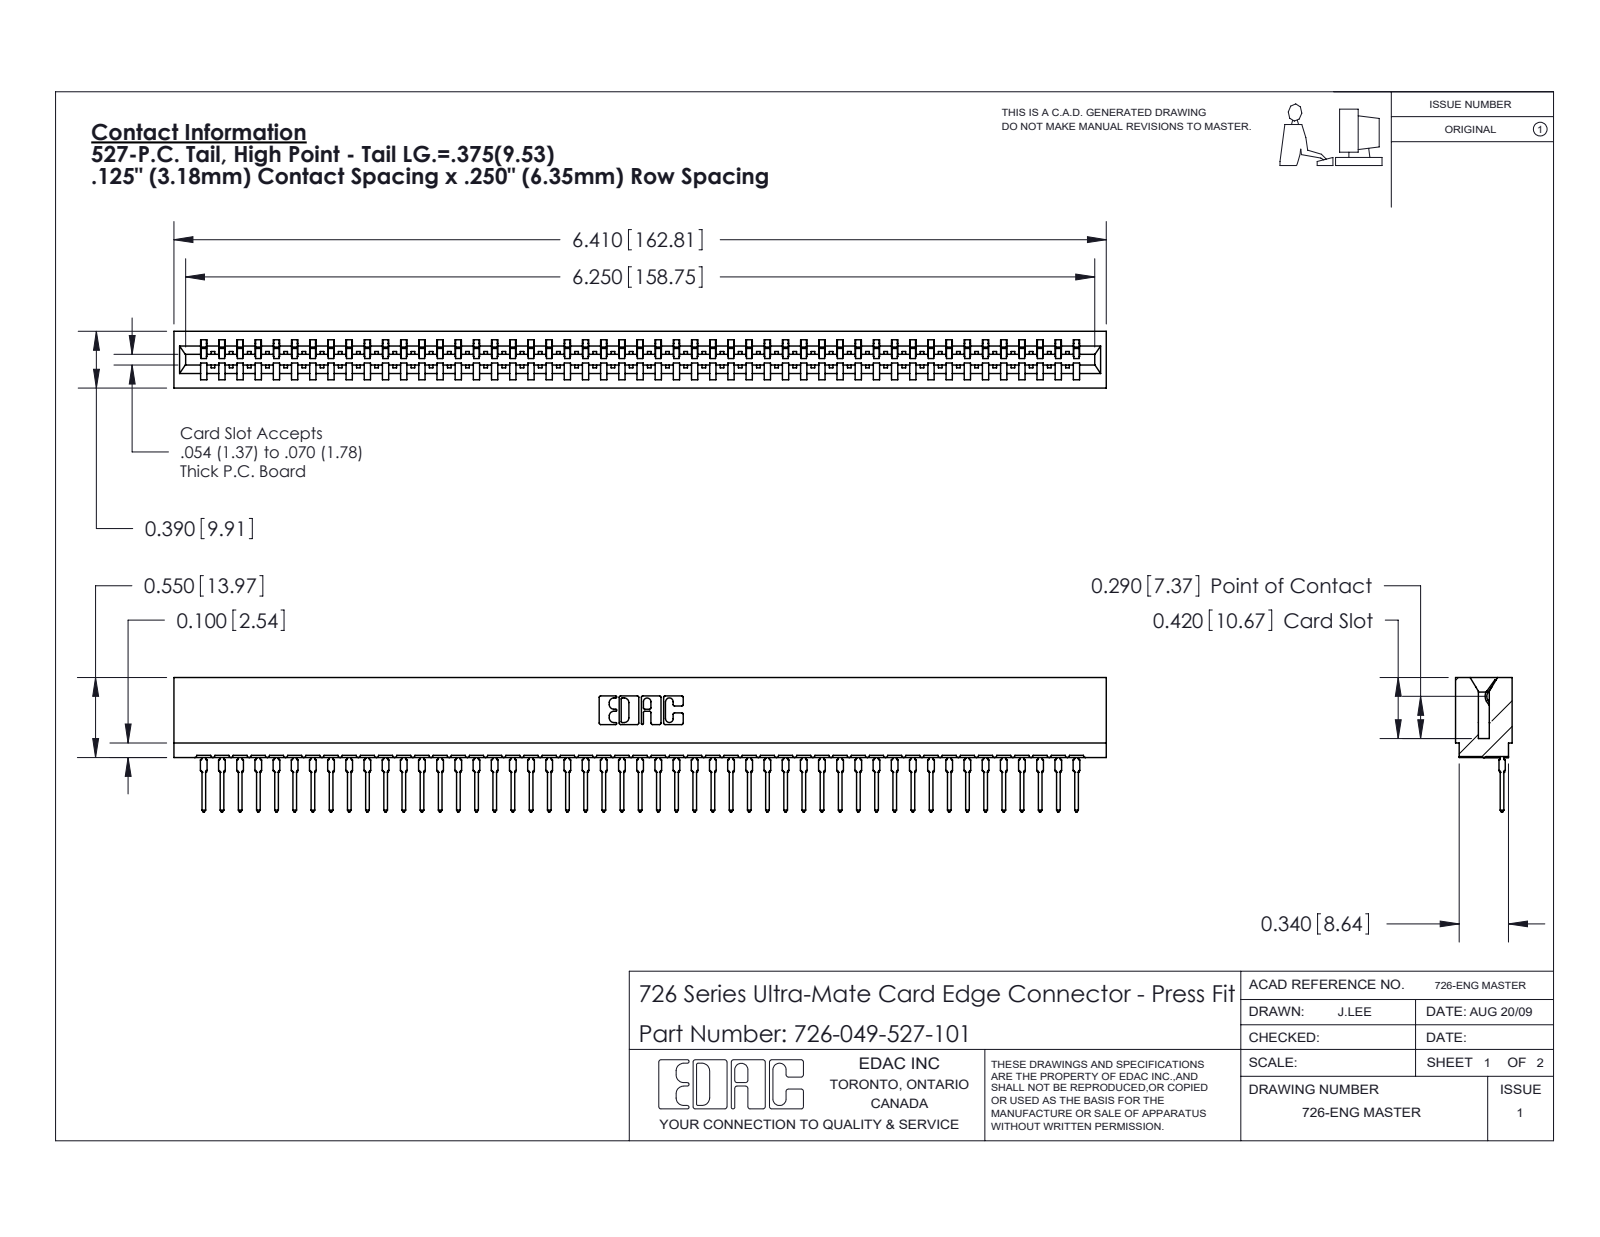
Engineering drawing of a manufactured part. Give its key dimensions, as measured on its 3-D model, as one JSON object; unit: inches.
{"part_name": "726 Part_.515 Slot Depth - 01; 726-049-527-101; 746-292-001_527", "step_written_by": "SolidWorks 2020 (CONFIG_CONTROL_DESIGN)", "units": "inches", "bodies": {"solids": 50, "faces": 5389, "planar": 3142, "cylindrical": 973, "other": 1274}, "overall_size": [6.41, 0.924, 0.39], "volume_in3": 0.888, "surface_area_in2": 35, "partial_cylinders_radius": [[0.021, 98], [0.015, 50], [0.01, 22], [0.007, 6], [0.031, 6], [0.005, 4], [0.011, 4], [0.026, 3]], "face_to_face_distances": [0.057, 0.333, 0.39, 0.025, 0.307, 0.275, 0.25, 0.083, 0.365, 0.032]}
